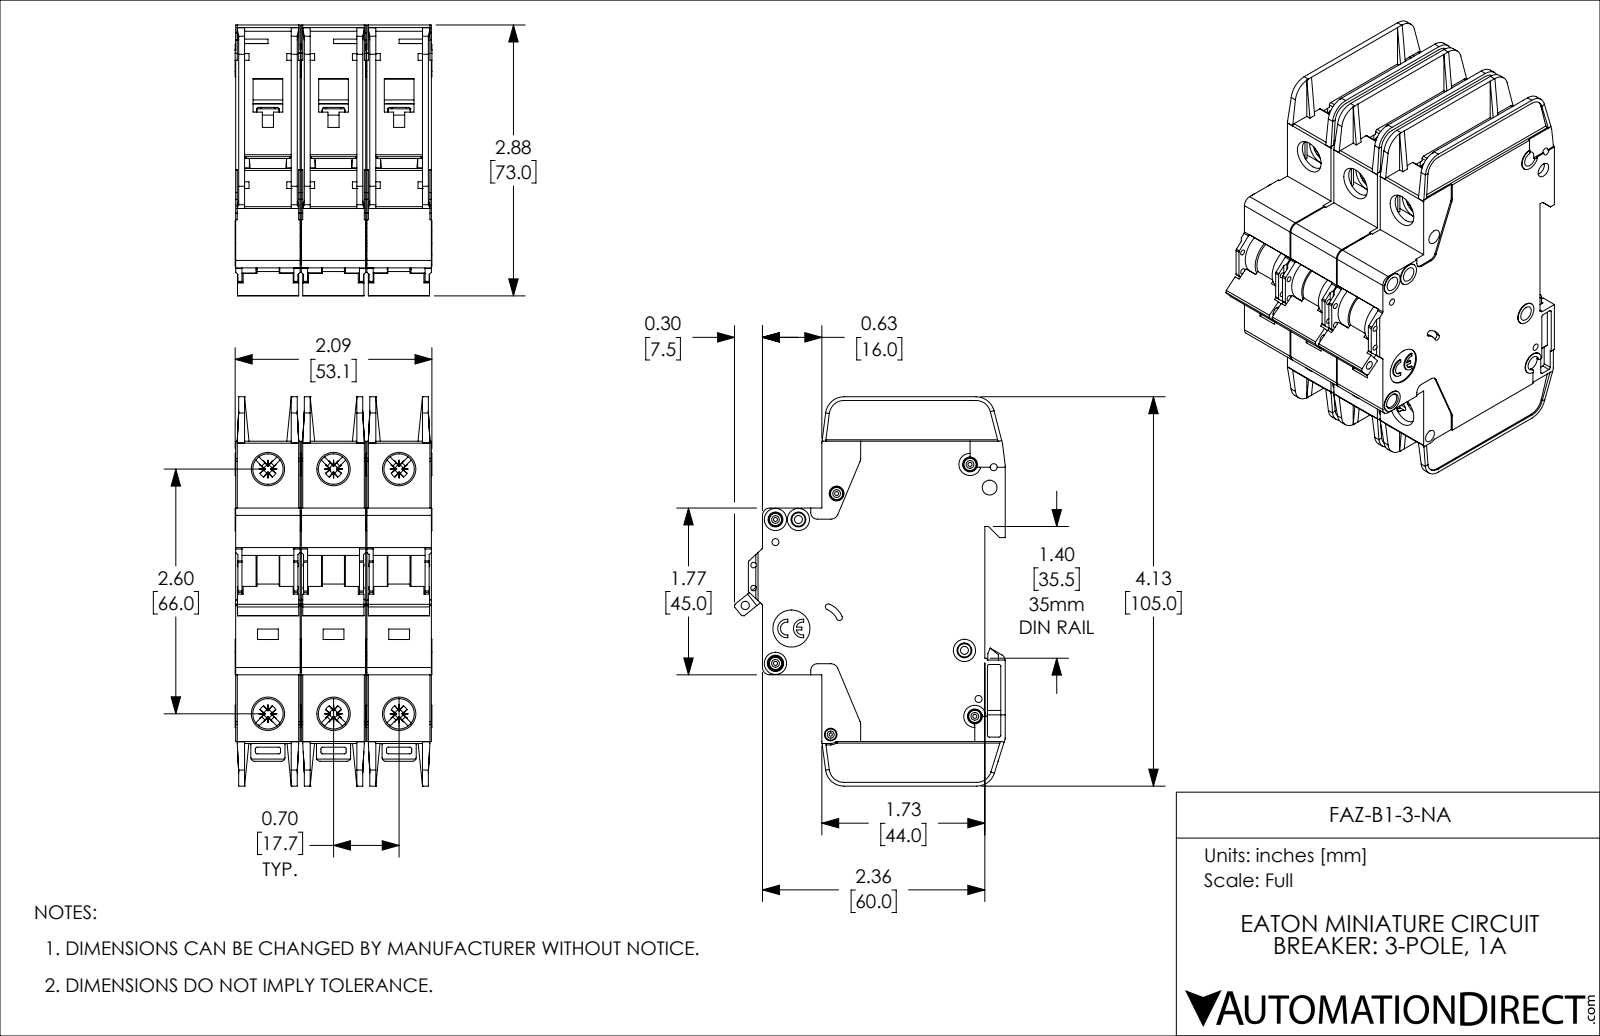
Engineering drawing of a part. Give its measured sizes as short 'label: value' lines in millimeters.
name: FAZ-B1-3-NA
written by: SolidWorks 2019 (AUTOMOTIVE_DESIGN)
unit: mm
bodies: 3 solids, 3381 faces (2013 planar, 1071 cylindrical, 297 other)
size: 105 × 73.1 × 53.1
volume: 230 200 mm³; area: 79 350 mm²
holes: 8× ⌀4, 6× ⌀8.2, 5× ⌀1.1, 4× ⌀1.9, 2× ⌀1.5, 2× ⌀2.2, 1× ⌀0.9, 1× ⌀2.3, 1× ⌀2.5, 1× ⌀3.4, 1× ⌀10
bosses: 5× ⌀3.3, 4× ⌀6, 4× ⌀3, 3× ⌀2.5
rounds: 72× R0.5, 30× R0.4, 18× R1, 12× R1.1, 12× R2, 6× R0.2, 6× R0.3, 6× R0.7
face distances: 17.7, 1.2, 35.4, 17.4, 15, 35.1, 18.9, 16.5, 2.7, 2.4
hole spacings: 17.7, 68.3, 66, 6.2, 13.6, 22.1, 35.4, 74.9
